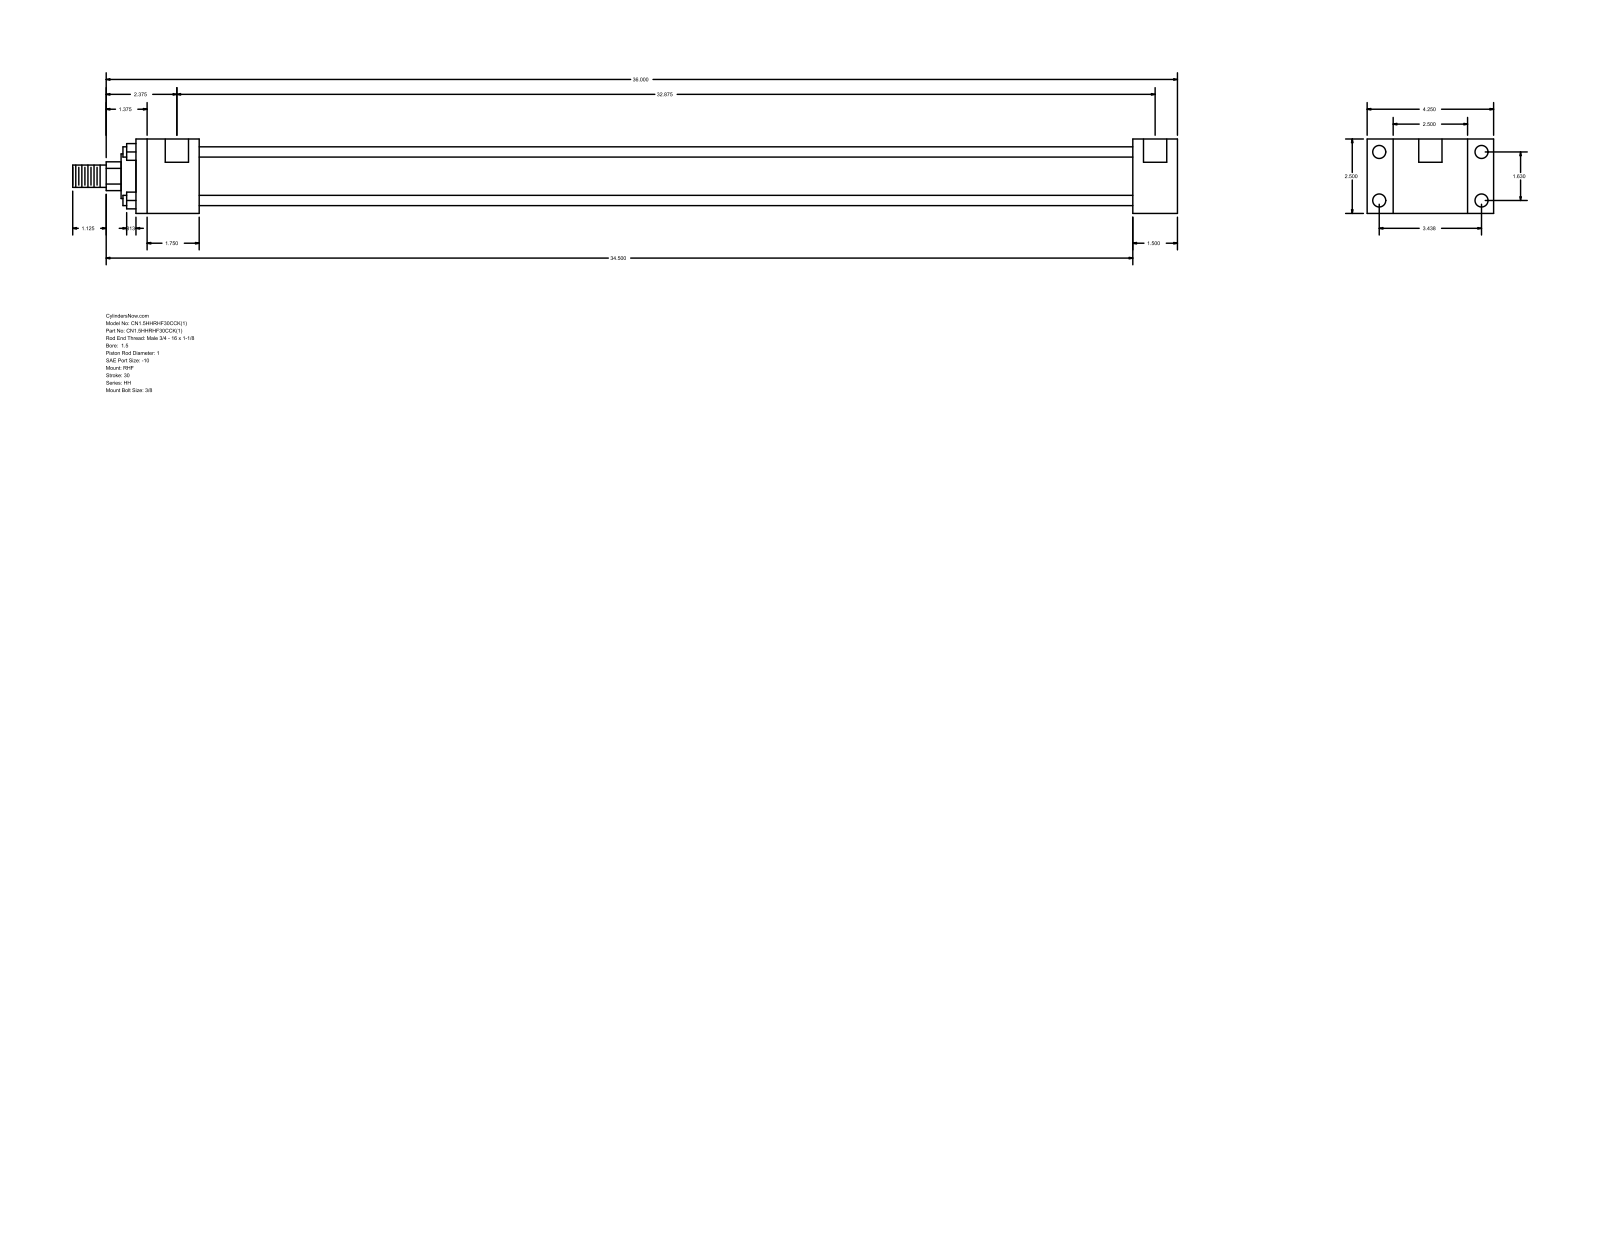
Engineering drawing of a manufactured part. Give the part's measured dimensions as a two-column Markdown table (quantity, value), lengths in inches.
| quantity | value |
| --- | --- |
| part name | HH_RHF__0150_1 |
| STEP written by | GSSL Pune (CONFIG_CONTROL_DESIGN) |
| units | inches |
| bodies | 0 solids, 88 faces (60 planar, 28 cylindrical, 0 other) |
| overall size | 37.125 × 4.25 × 2.5 |
| round holes (diameter × count) | 0.219 × 4, 0.438 × 4, 0.781 × 2 |
| round bosses / shafts (diameter × count) | 0.345 × 4, 1.75 × 1, 1.5 × 1, 1 × 1, 0.75 × 1 |
| partial cylindrical surfaces (radius × count) | 0.484 × 1 |
| main face-to-face distances | 2.5, 0.875, 3.375, 1.5, 4.25, 31.375, 32.875, 2.125, 33.5, 35 |
| hole center spacings | 0.063, 1.63, 3.438, 3.805, 32.937, 33, 32.875 |
